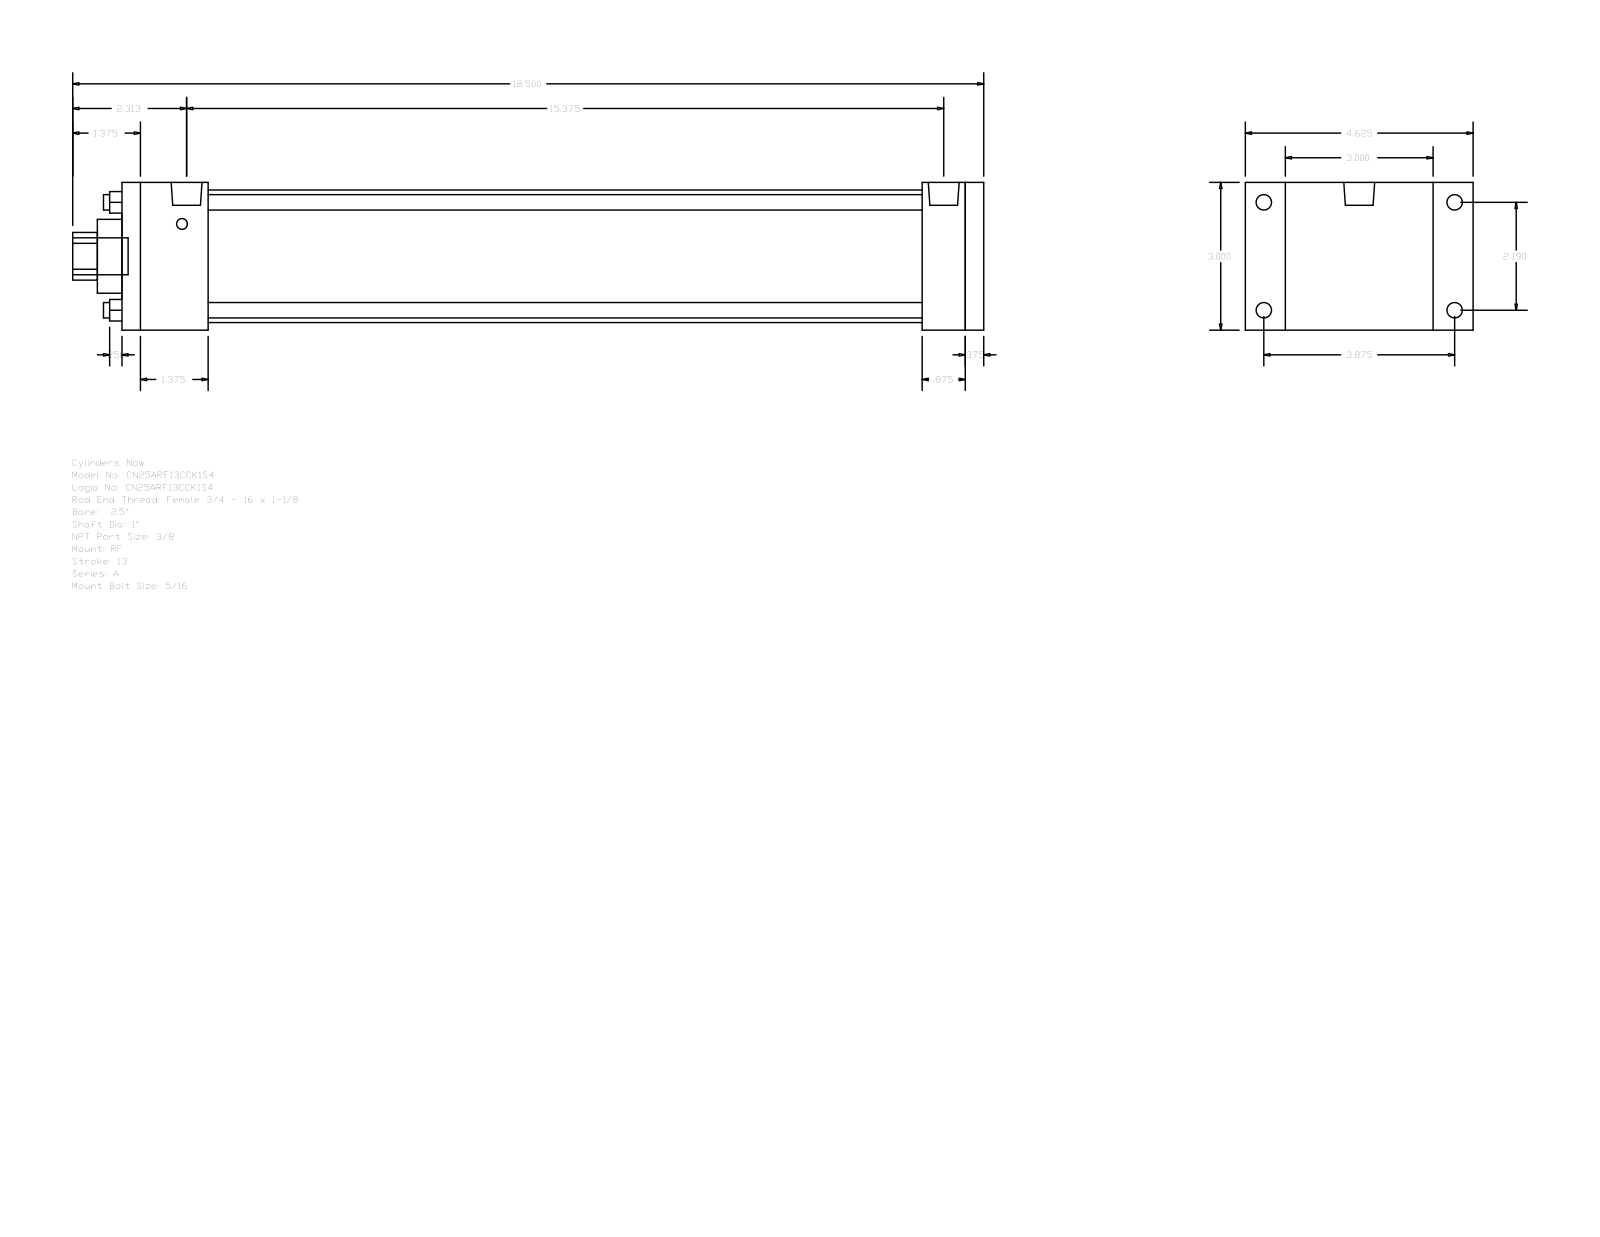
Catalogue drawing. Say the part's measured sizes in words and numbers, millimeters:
The part is named "A_RF__0250_1". Its 3-D file was written by "GSSL Pune (CONFIG_CONTROL_DESIGN)". It is 0 solids with 92 faces: 64 planar, 28 cylindrical and 0 other. Overall it measures 469.9 by 117.47 by 76.2 millimeters. Round holes: 4 of diameter 7.94, 1 of diameter 25.4, 1 of diameter 38.1, 1 of diameter 68.33. Round bosses or shafts: 4 of diameter 7.94, 4 of diameter 5.56, 2 of diameter 15.93, 1 of diameter 19.05. Partial cylindrical surfaces (rounded edges, fillets, slot ends): 1 of radius 12.29. The main face-to-face distances are 76.2, 444.5, 9.52, 434.98, 44.45, 412.75, 368.3, 390.53, 400.05, 22.23. The hole center spacings are 39.33, 55.62, 78.66.
